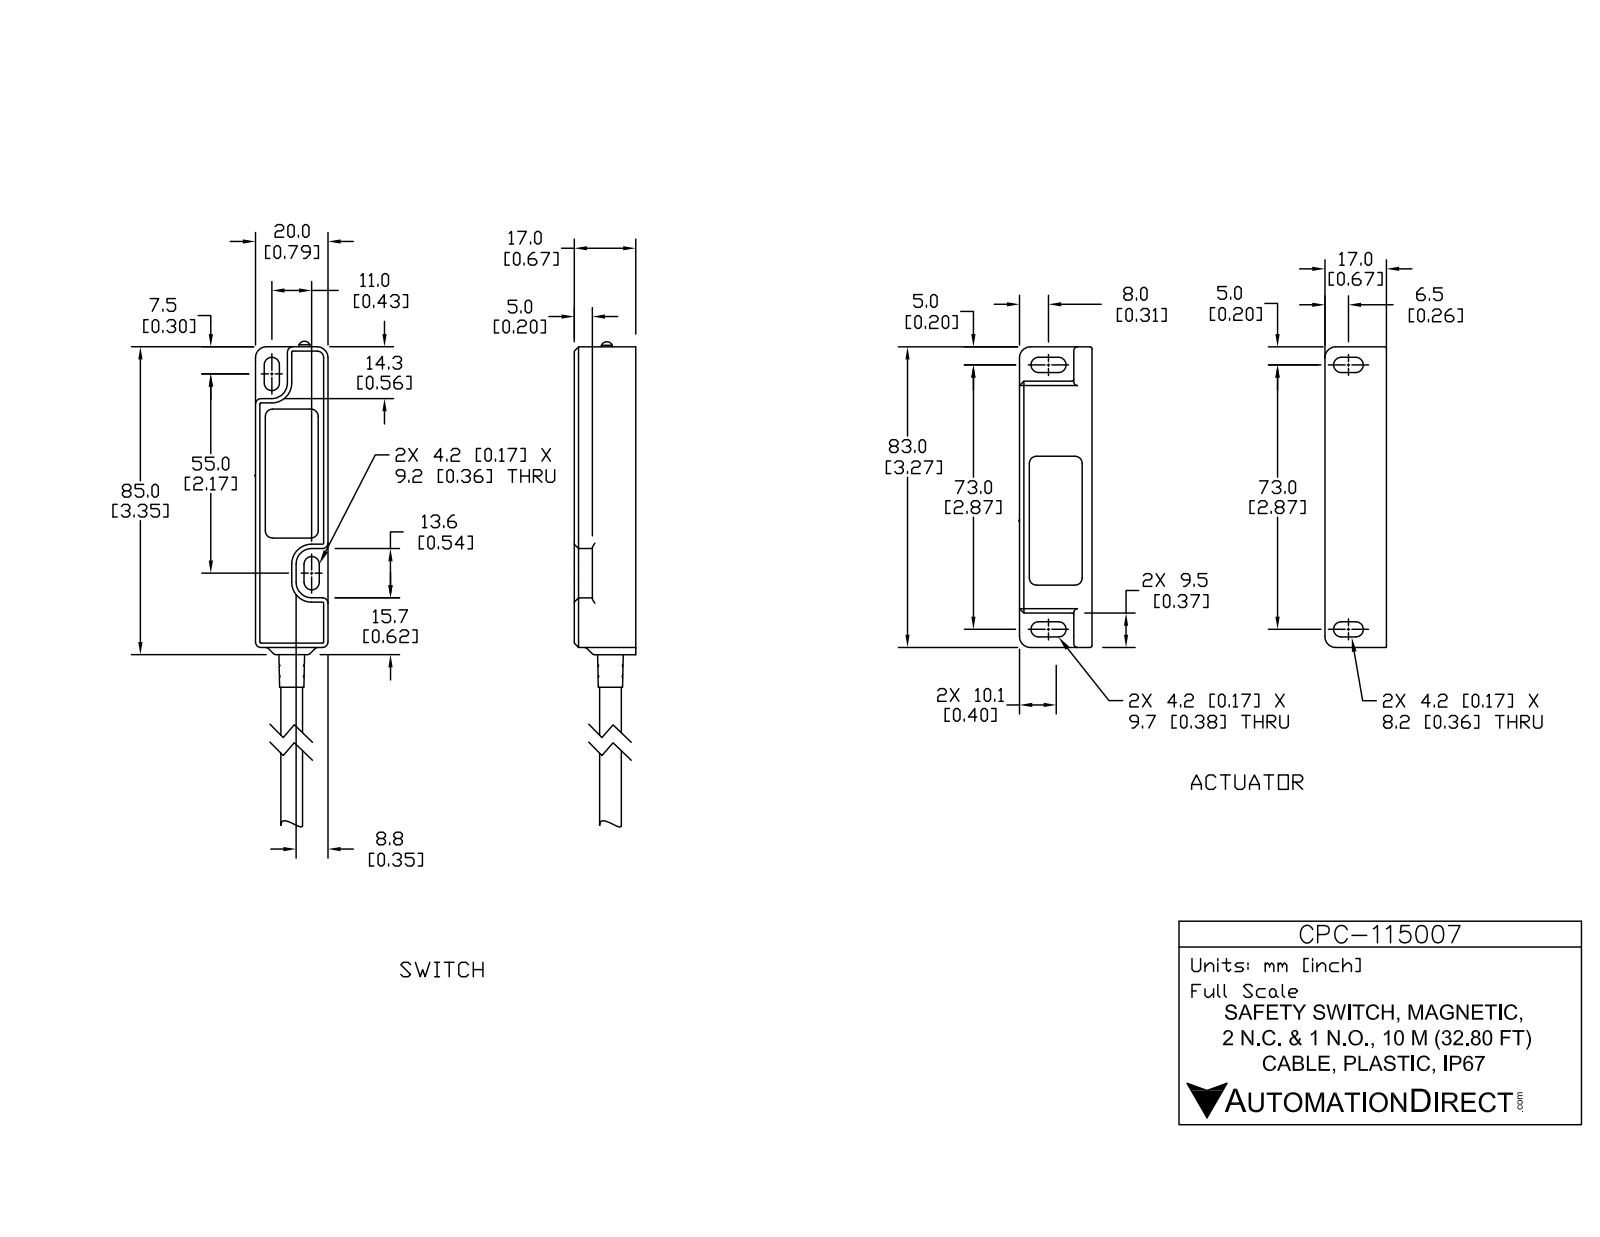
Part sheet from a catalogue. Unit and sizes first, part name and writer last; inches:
Units: inches
Overall size (bounding box): 7.267 × 1.614 × 0.669
Round bosses / shafts (diameter × count): ⌀0.236 ×1, ⌀0.118 ×1
Partial cylindrical surfaces — rounded edges, fillets, slot ends (radius × count): R0.083 ×12, R0.039 ×10, R0.02 ×8, R0.079 ×8, R0.059 ×6, R0.118 ×6, R0.028 ×3, R0.169 ×3
Main face-to-face distances: 0.827, 0.787, 0.669, 1.614, 0.657, 0.039, 0.197, 0.472, 0.374, 2.894
Volume: 3.242 in³ · Surface area: 25.14 in²
Bodies: 5 solids, 199 faces (78 planar, 71 cylindrical, 50 other)
Part name (STEP PRODUCT): CPC-115007; CPC-115007_2; CPC-115007_1
STEP written by: SolidWorks 2017 (AUTOMOTIVE_DESIGN)
